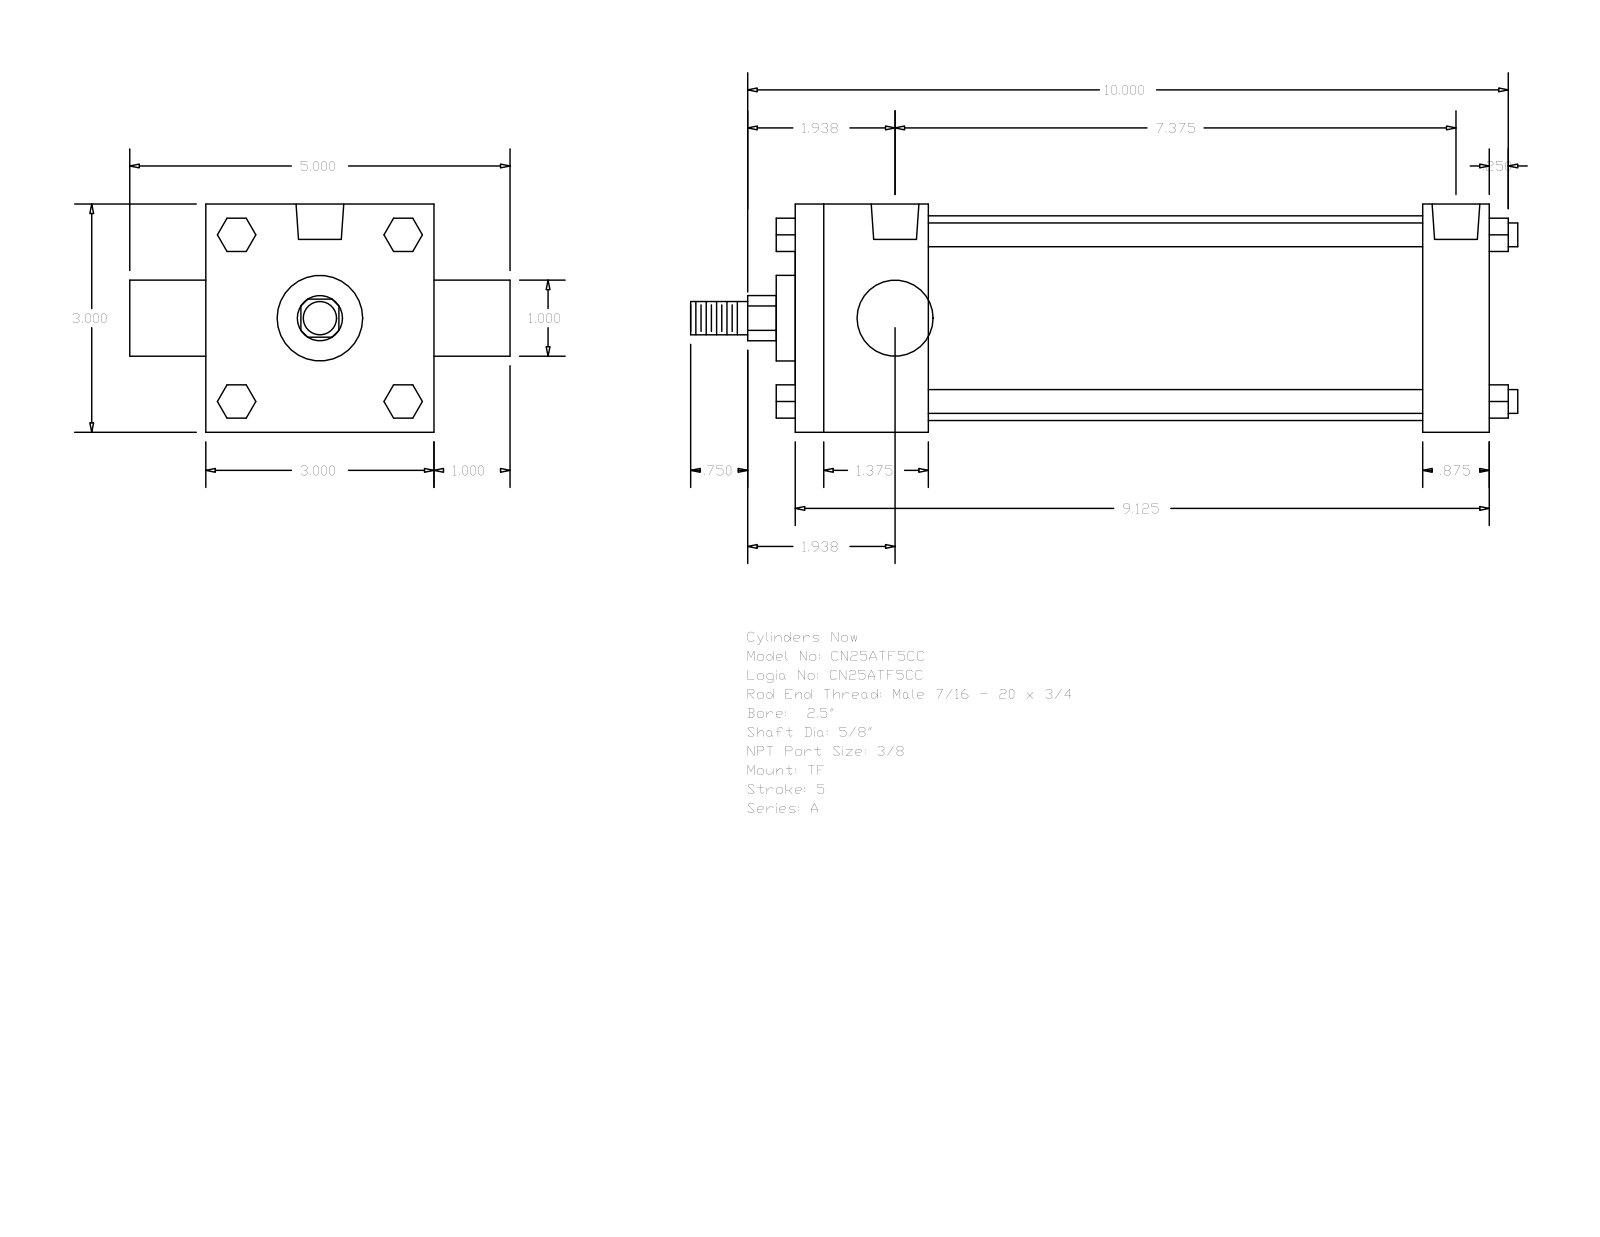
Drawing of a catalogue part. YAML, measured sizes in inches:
part_name: "A_TF__0250_0.625"
step_written_by: "GSSL Pune (CONFIG_CONTROL_DESIGN)"
units: inches
bodies: {solids: 0, faces: 120, planar: 92, cylindrical: 28, other: 0}
overall_size: [10.875, 5, 3]
round_holes:
  - {diameter: 0.219, count: 3}
  - {diameter: 0.627, count: 2}
round_bosses_or_shafts:
  - {diameter: 0.313, count: 4}
  - {diameter: 2.69, count: 1}
  - {diameter: 1.125, count: 1}
  - {diameter: 1, count: 1}
  - {diameter: 0.625, count: 1}
  - {diameter: 0.437, count: 1}
partial_cylinders:
  - {radius: 0.297, count: 1}
face_to_face_distances: [3, 9.125, 1.75, 8.25, 6.5, 7.375, 0.875, 1, 4, 0.25]
hole_center_spacings: [0.094, 7.469, 7.375, 7.563]
